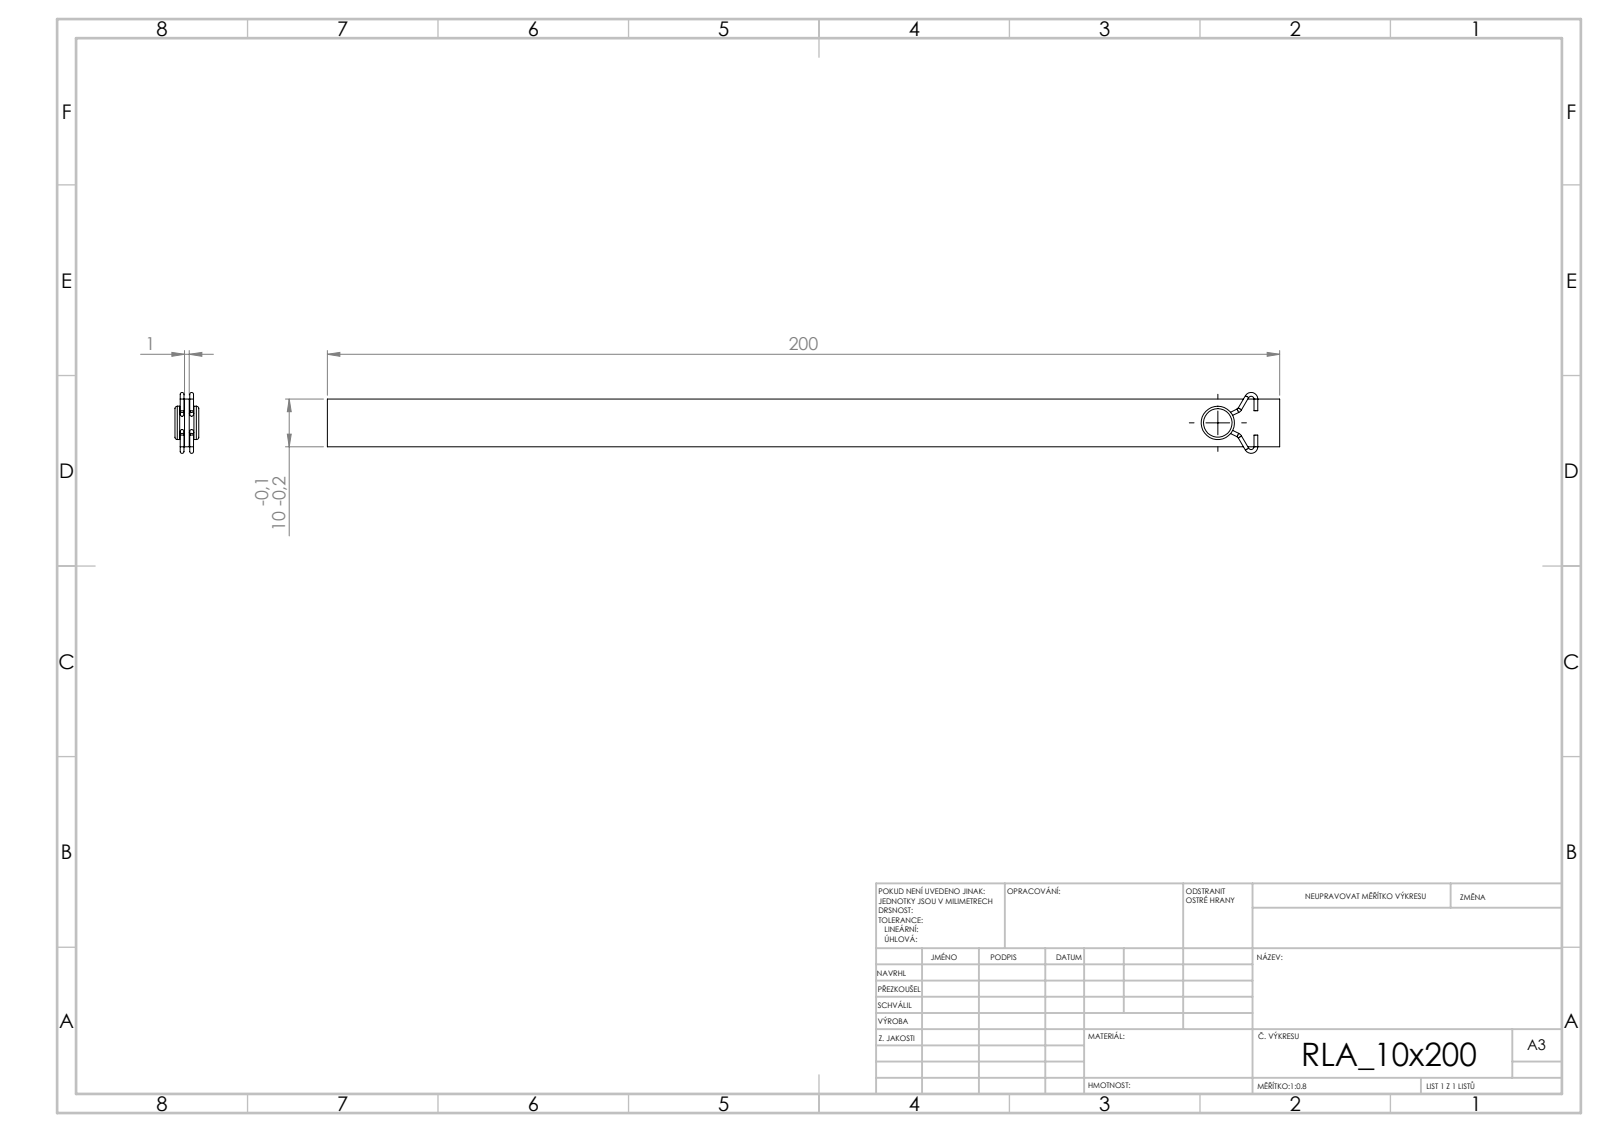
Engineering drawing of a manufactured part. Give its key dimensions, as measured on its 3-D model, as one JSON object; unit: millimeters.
{"step_written_by": "SolidWorks 2019 (CONFIG_CONTROL_DESIGN)", "units": "millimeters", "bodies": {"solids": 3, "faces": 82, "planar": 14, "cylindrical": 40, "other": 28}, "overall_size": [200, 12.8, 5], "volume_mm3": 2134, "surface_area_mm2": 4757, "round_bosses_or_shafts": [[0.8, 14], [7, 1], [4, 1]], "face_to_face_distances": [1, 10, 2, 3, 4, 5, 200, 2.45, 7.55, 5.1]}
